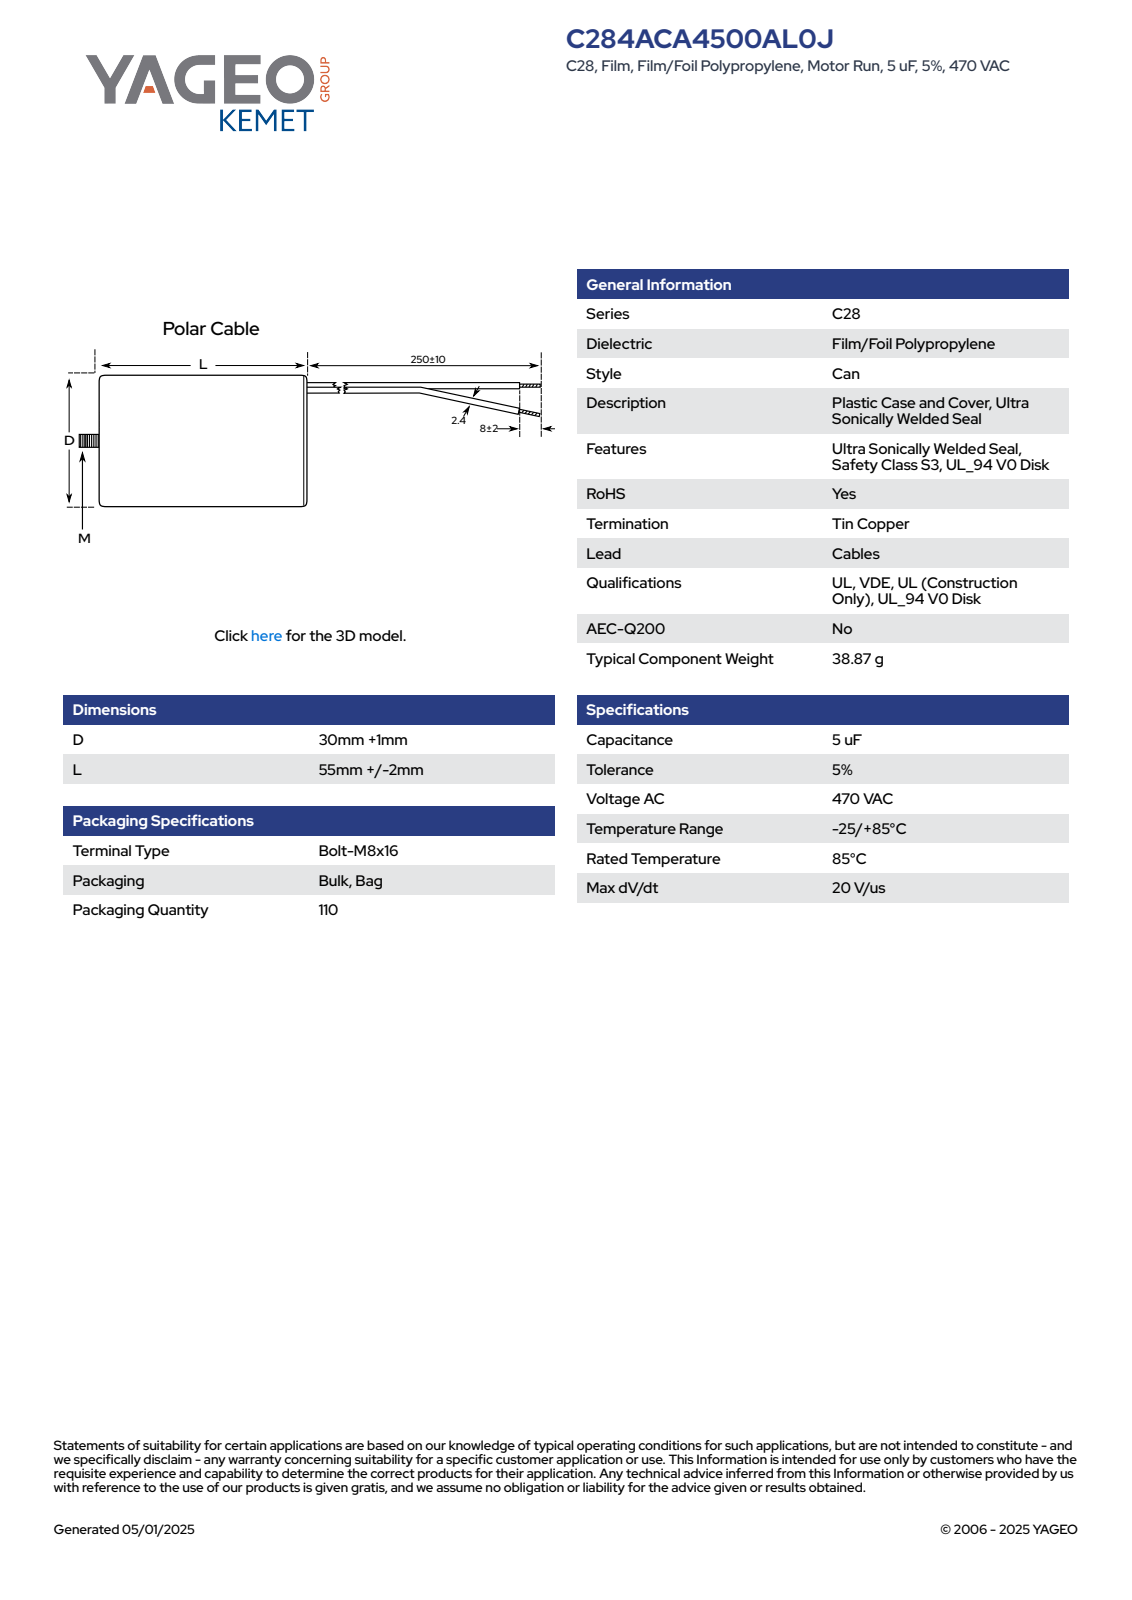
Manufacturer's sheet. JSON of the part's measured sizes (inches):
{"part_name": "CFM_KC28P_30X55_D31L57", "step_written_by": "SolidWorks 2014 (AUTOMOTIVE_DESIGN)", "units": "inches", "bodies": {"solids": 1, "faces": 76, "planar": 26, "cylindrical": 15, "other": 35}, "overall_size": [2.638, 1.221, 1.22], "volume_in3": 2.584, "surface_area_in2": 11.47, "round_holes": [[1.063, 1]], "round_bosses_or_shafts": [[1.22, 1], [0.315, 1]], "partial_cylinders_radius": [[0.611, 1]], "face_to_face_distances": [2.165, 2.244, 0.079, 0.394, 2.559, 2.638]}
